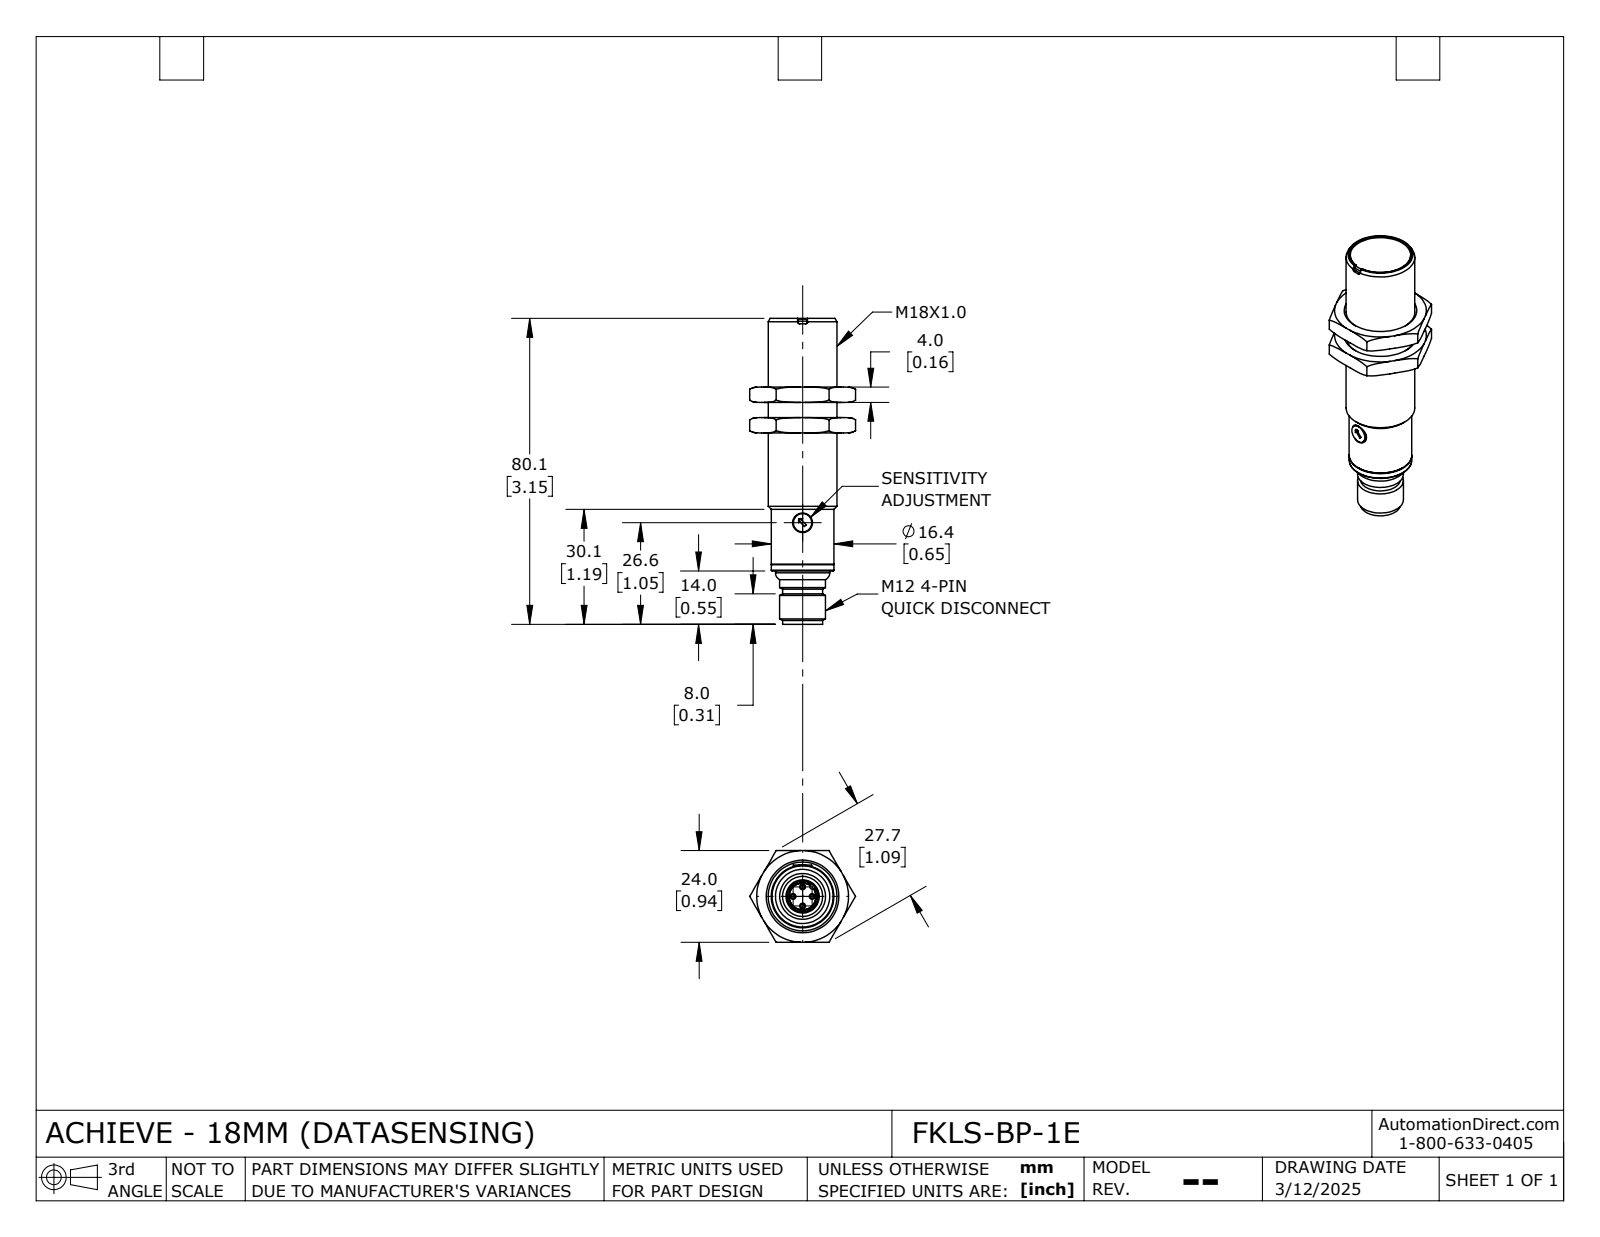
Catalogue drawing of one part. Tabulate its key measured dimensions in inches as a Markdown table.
| quantity | value |
| --- | --- |
| part name | FKLS-BP-1E_Default |
| STEP written by | SolidWorks 2024 (CONFIG_CONTROL_DESIGN) |
| units | inches |
| bodies | 4 solids, 135 faces (54 planar, 29 cylindrical, 52 other) |
| overall size | 3.154 × 1.091 × 0.945 |
| volume | 1.259 in³ |
| surface area | 12.98 in² |
| round holes (diameter × count) | 0.106 × 1, 0.185 × 1, 0.278 × 1, 0.327 × 1, 0.622 × 1, 0.709 × 1 |
| round bosses / shafts (diameter × count) | 0.039 × 4, 0.646 × 1, 0.559 × 1, 0.472 × 1, 0.413 × 1, 0.276 × 1, 0.189 × 1 |
| partial cylindrical surfaces (radius × count) | 0.02 × 4, 0.024 × 1, 0.331 × 1 |
| main face-to-face distances | 0.157, 0.315, 0.945, 0.472, 0.055, 0.348, 0.403, 0.612, 0.96, 1.015 |
